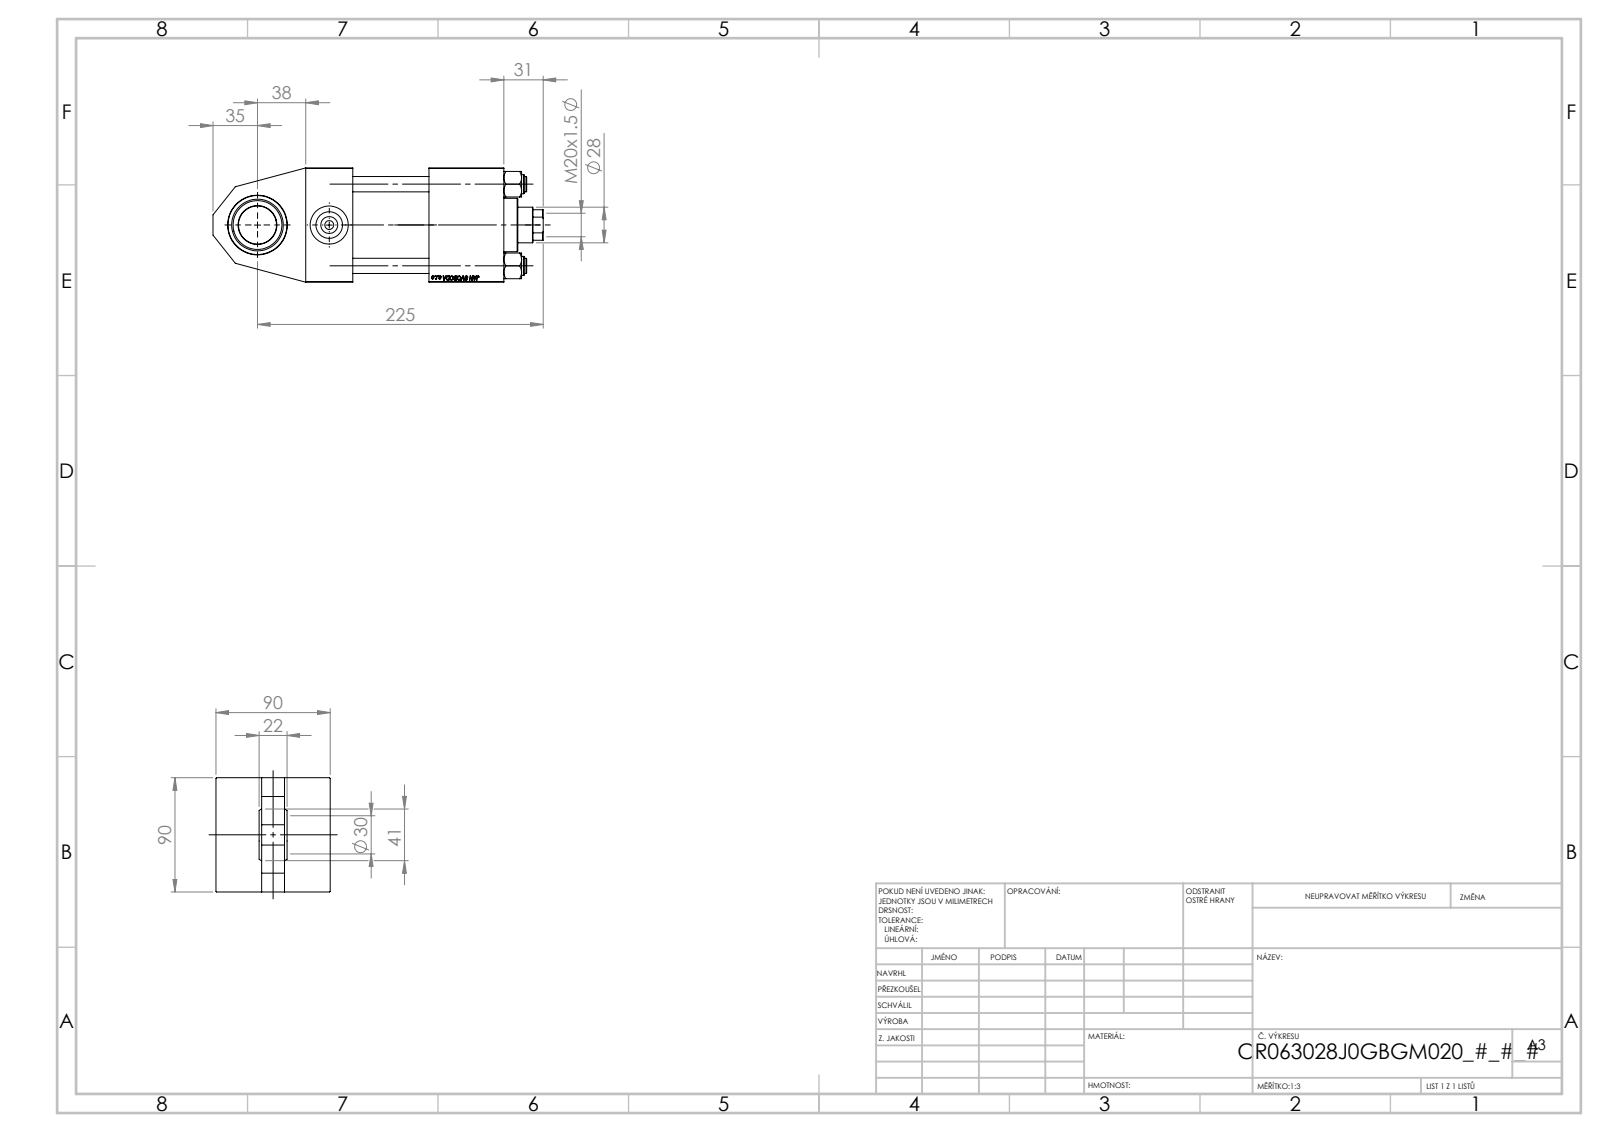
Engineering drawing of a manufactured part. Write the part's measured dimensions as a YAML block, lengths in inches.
part_name: "V215CR_J_VNITRNI_KROUZEK; V215_VC_A; V215CR_VCP_J; NUT_M5_J (+2 more)"
step_written_by: "SolidWorks 2019 (CONFIG_CONTROL_DESIGN)"
units: inches
bodies: {solids: 12, faces: 1145, planar: 516, cylindrical: 89, other: 540}
overall_size: [10.236, 3.543, 3.543]
volume: 62.98
surface_area: 310.1
round_holes:
  - {diameter: 0.472, count: 4}
  - {diameter: 1.181, count: 3}
  - {diameter: 0.098, count: 2}
  - {diameter: 0.276, count: 2}
  - {diameter: 0.825, count: 2}
  - {diameter: 0.728, count: 1}
  - {diameter: 1.102, count: 1}
  - {diameter: 1.22, count: 1}
  - {diameter: 1.85, count: 1}
  - {diameter: 1.969, count: 1}
  - {diameter: 2.362, count: 1}
  - {diameter: 2.48, count: 1}
round_bosses_or_shafts:
  - {diameter: 0.591, count: 4}
  - {diameter: 2.717, count: 1}
  - {diameter: 1.654, count: 1}
partial_cylinders:
  - {radius: 0.531, count: 1}
face_to_face_distances: [3.543, 2.126, 1.417, 4.685, 1.457, 6.142, 3.819, 2.362, 2.323, 0.709]
hole_center_spacings: [1.275, 1.79, 2.531, 2.694, 1.112, 2.224, 3.58, 3.878]
